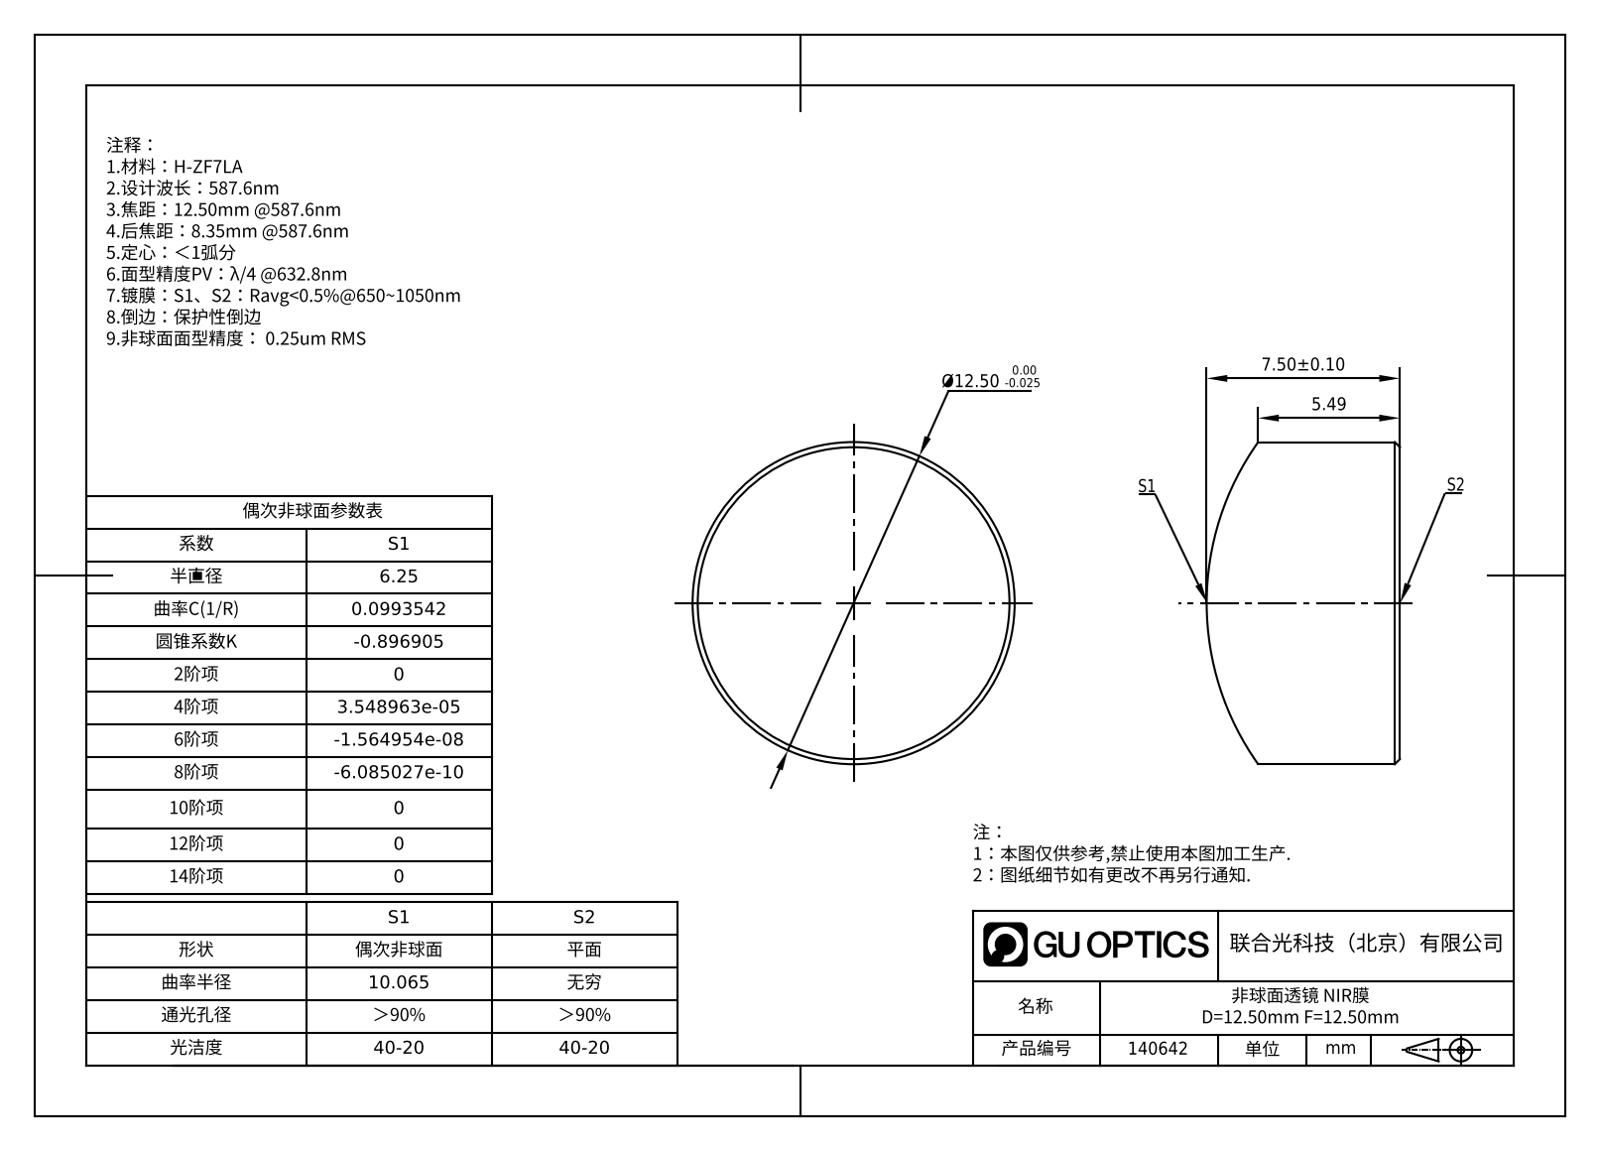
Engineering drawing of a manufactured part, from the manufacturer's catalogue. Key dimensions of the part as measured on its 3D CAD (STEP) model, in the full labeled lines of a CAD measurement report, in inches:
Part name (STEP PRODUCT): GLA11-012-012-H-VIS
STEP written by: SolidWorks 2022 (AUTOMOTIVE_DESIGN)
Units: inches
Bodies: 1 solid, 7 faces (1 planar, 2 cylindrical, 4 other)
Overall size (bounding box): 0.492 × 0.492 × 0.295
Volume: 0.049 in³ · Surface area: 0.727 in²
Round bosses / shafts (diameter × count): ⌀0.492 ×1
